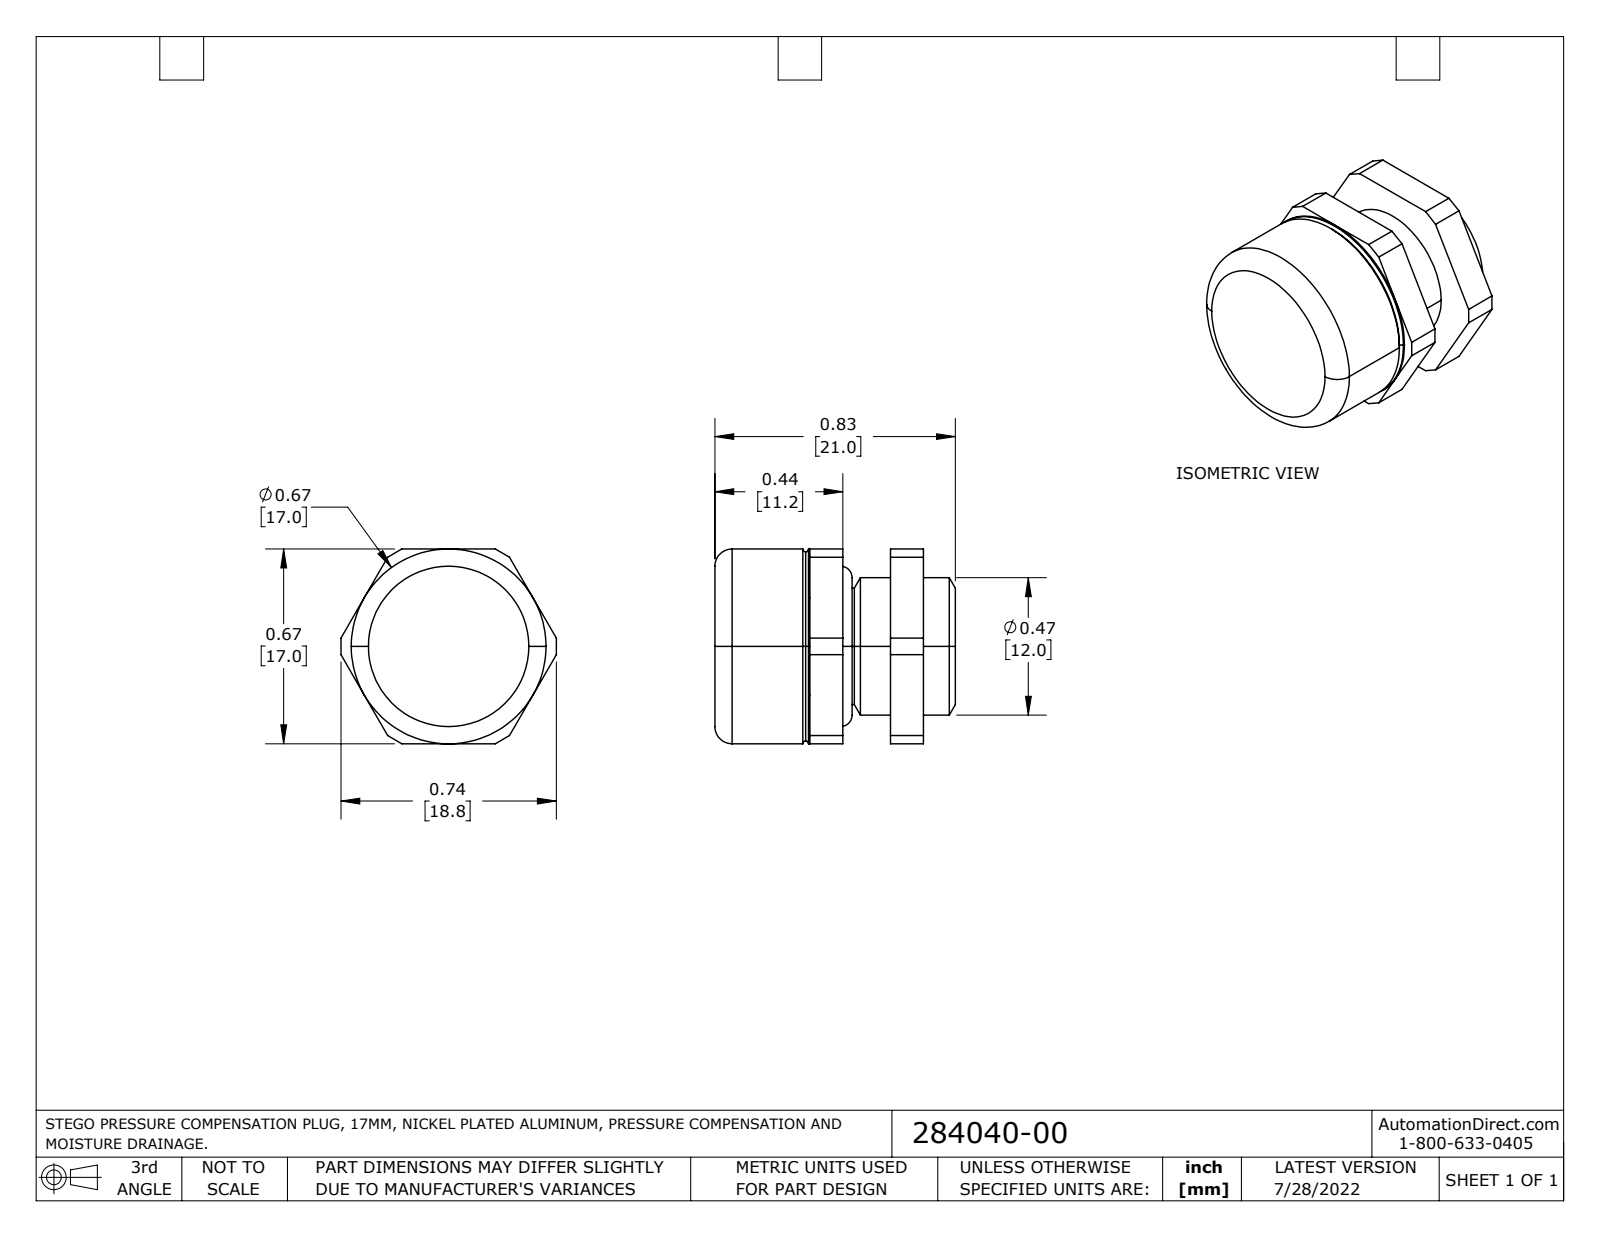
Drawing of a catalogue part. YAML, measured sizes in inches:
part_name: "284040-00"
step_written_by: "SolidWorks 2021 (AUTOMOTIVE_DESIGN)"
units: inches
bodies: {solids: 1, faces: 57, planar: 35, cylindrical: 10, other: 12}
overall_size: [0.827, 0.74, 0.669]
volume: 0.248
surface_area: 2.836
round_bosses_or_shafts:
  - {diameter: 0.669, count: 1}
  - {diameter: 0.472, count: 1}
  - {diameter: 0.4, count: 1}
face_to_face_distances: [0.669, 0.717, 0.113, 0.604, 0.277, 0.164, 0.44, 0.11, 0.223, 0.387]
